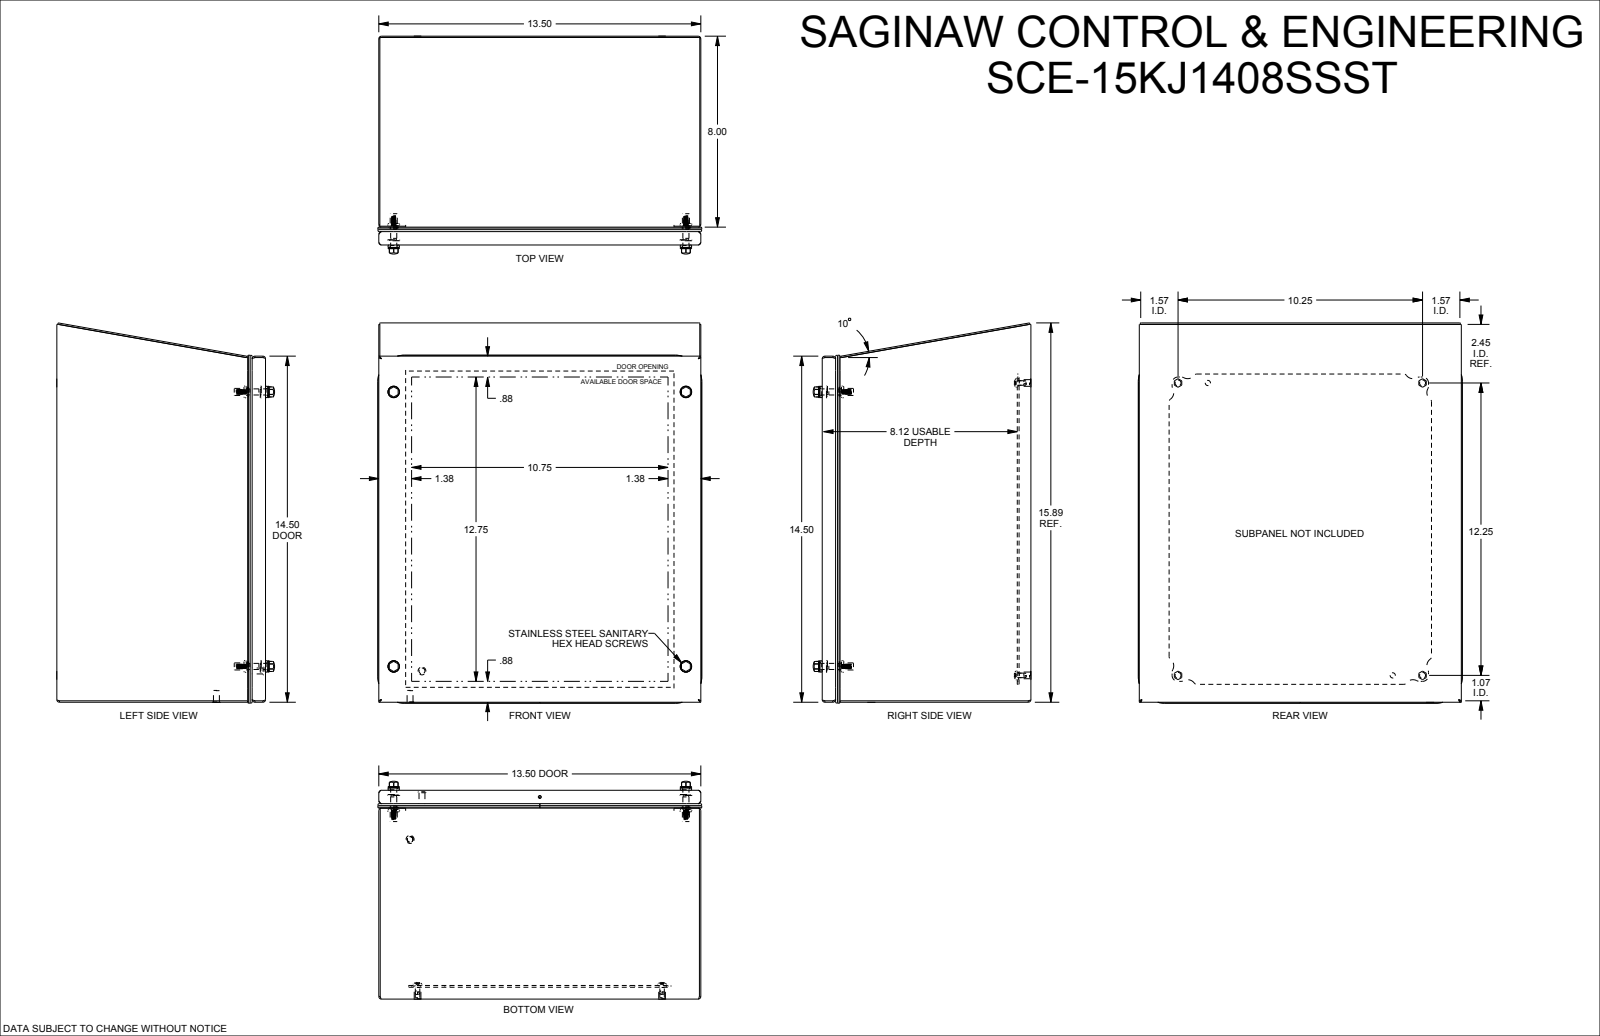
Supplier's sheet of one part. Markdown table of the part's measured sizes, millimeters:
| quantity | value |
| --- | --- |
| part name | SCE-15KJ1408SSST |
| STEP written by | SolidWorks 2021 (AUTOMOTIVE_DESIGN) |
| units | millimeters |
| bodies | 31 solids, 991 faces (349 planar, 309 cylindrical, 333 other) |
| overall size | 404.1 × 345 × 232 |
| volume | 1 340 000 mm³ |
| surface area | 1 594 000 mm² |
| round holes (diameter × count) | 4.8 × 8, 7.1 × 8, 6.4 × 4, 6.9 × 4, 8.1 × 4, 9.3 × 4, 5.5 × 2 |
| round bosses / shafts (diameter × count) | 12.7 × 4, 12.1 × 4, 9.5 × 4, 7.5 × 4, 7.1 × 4, 6.5 × 4, 5.8 × 4, 4.8 × 4 |
| partial cylindrical surfaces (radius × count) | 1.3 × 26, 2.8 × 26, 0.5 × 20, 3.2 × 12, 6.4 × 12, 8.7 × 8, 0.1 × 4, 0.3 × 4 |
| main face-to-face distances | 1.5, 220.7, 341.4, 219.2, 222.2, 208.1, 209.6, 14.5, 13, 206.2 |
| hole center spacings | 292.1, 311.2, 285.8, 302.7, 415.4, 415.5, 27.1, 260.2 |
